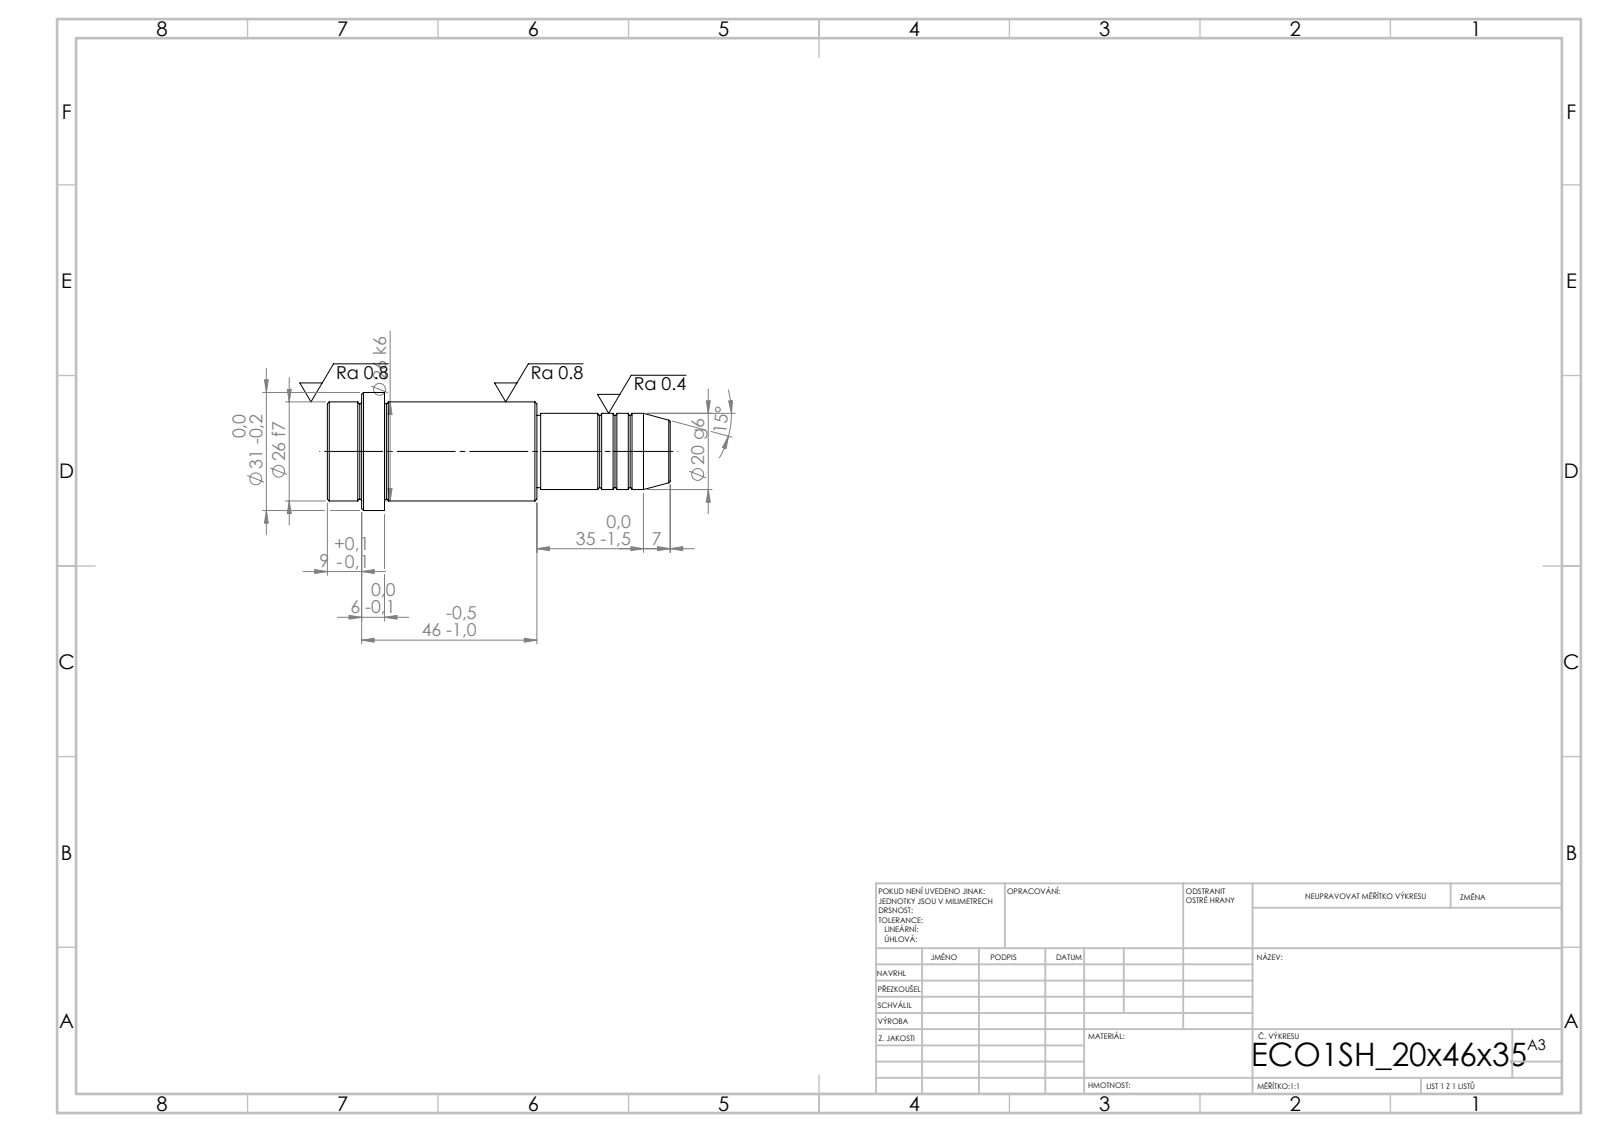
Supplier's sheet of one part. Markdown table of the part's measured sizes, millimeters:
| quantity | value |
| --- | --- |
| STEP written by | SolidWorks 2019 (CONFIG_CONTROL_DESIGN) |
| units | millimeters |
| bodies | 1 solid, 52 faces (6 planar, 16 cylindrical, 30 other) |
| overall size | 90 × 31 × 31 |
| volume | 40 953 mm³ |
| surface area | 8 321 mm² |
| round bosses / shafts (diameter × count) | 31 × 1, 26 × 1, 20 × 1, 19 × 1 |
| main face-to-face distances | 15, 40, 55, 35, 75, 90, 81, 46, 6, 9 |
